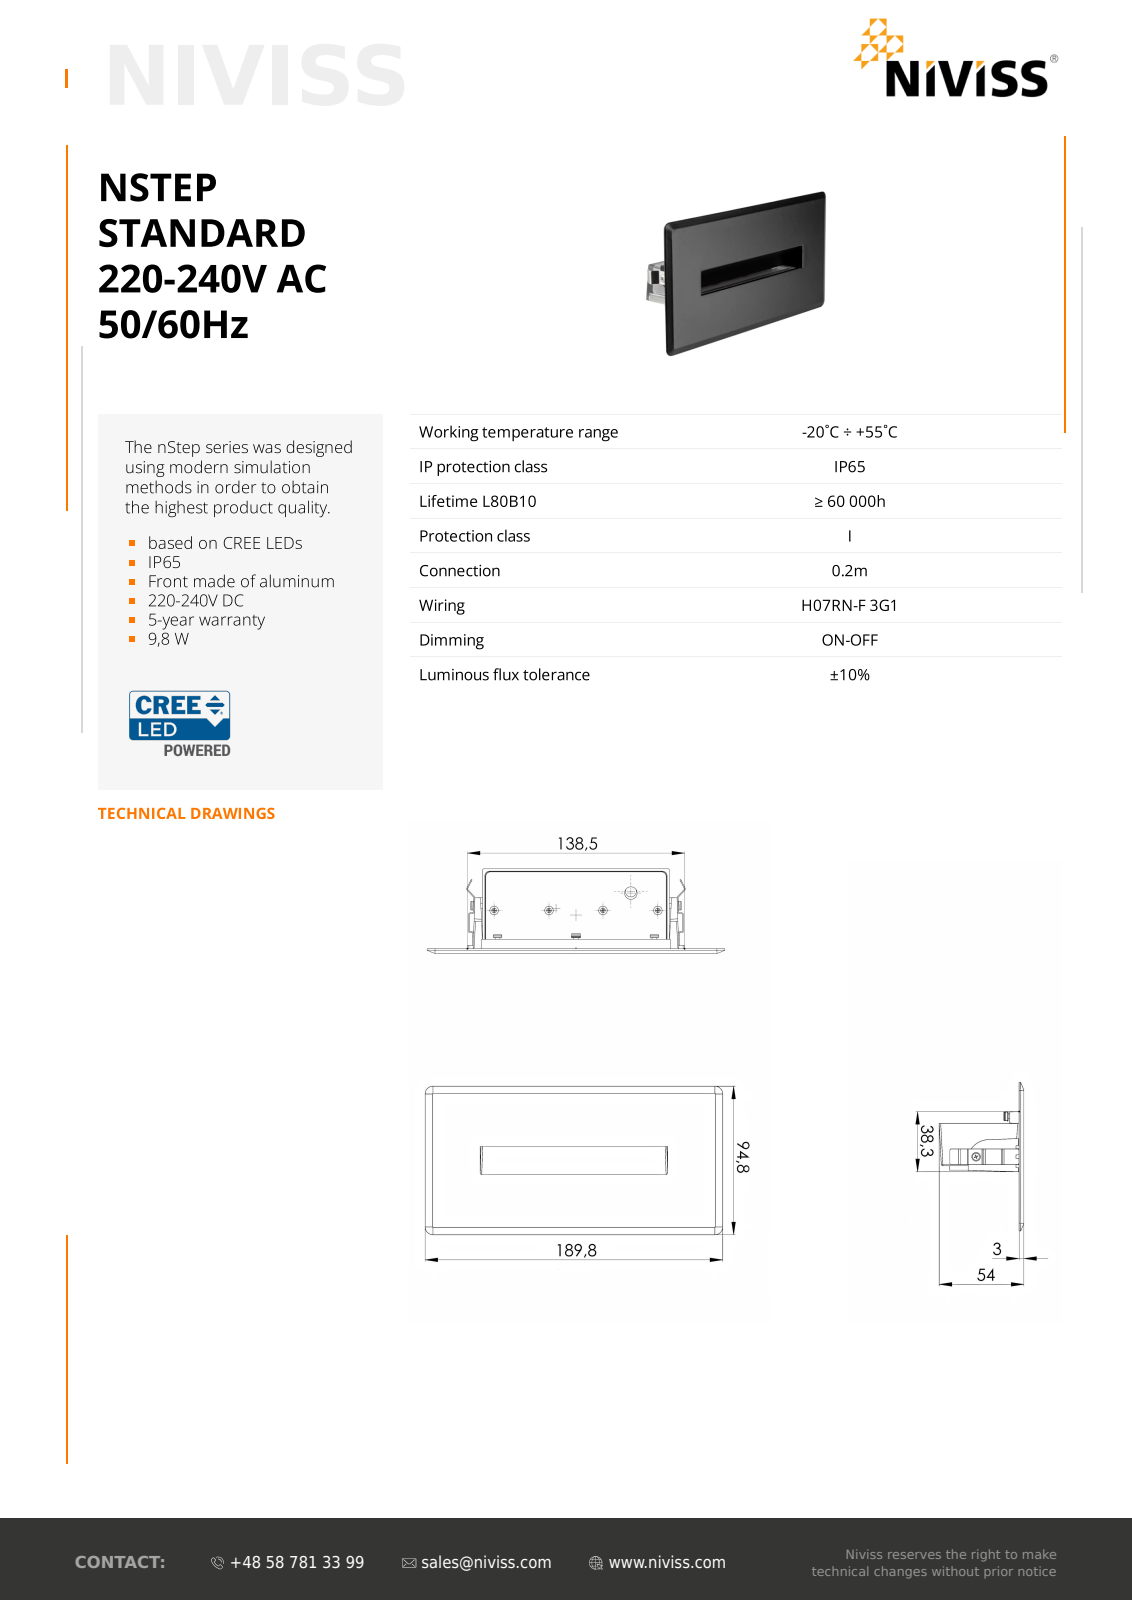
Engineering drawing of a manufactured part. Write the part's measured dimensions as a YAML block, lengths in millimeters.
part_name: "DK190806DD01A"
step_written_by: "SolidWorks 2017 (AUTOMOTIVE_DESIGN)"
units: millimeters
bodies: {solids: 48, faces: 2160, planar: 1273, cylindrical: 455, other: 432}
overall_size: [189.77, 94.77, 54]
volume: 136364
surface_area: 102766
round_holes:
  - {diameter: 2.5, count: 10}
  - {diameter: 3.5, count: 7}
  - {diameter: 3.2, count: 3}
  - {diameter: 7, count: 1}
  - {diameter: 8, count: 1}
  - {diameter: 11, count: 1}
round_bosses_or_shafts:
  - {diameter: 5.5, count: 9}
  - {diameter: 3, count: 5}
  - {diameter: 2.9, count: 4}
  - {diameter: 16, count: 1}
  - {diameter: 6, count: 1}
partial_cylinders:
  - {radius: 1, count: 42}
  - {radius: 0.7, count: 12}
  - {radius: 2, count: 12}
  - {radius: 1.3, count: 10}
  - {radius: 3, count: 8}
  - {radius: 0.1, count: 6}
  - {radius: 0.3, count: 4}
  - {radius: 5, count: 4}
face_to_face_distances: [3, 1.59, 23.09, 21.5, 2, 21.2, 1.89, 19, 18.7, 2.5]
hole_center_spacings: [50, 0.69, 17.44, 35, 52.28, 69.4, 1, 2]
